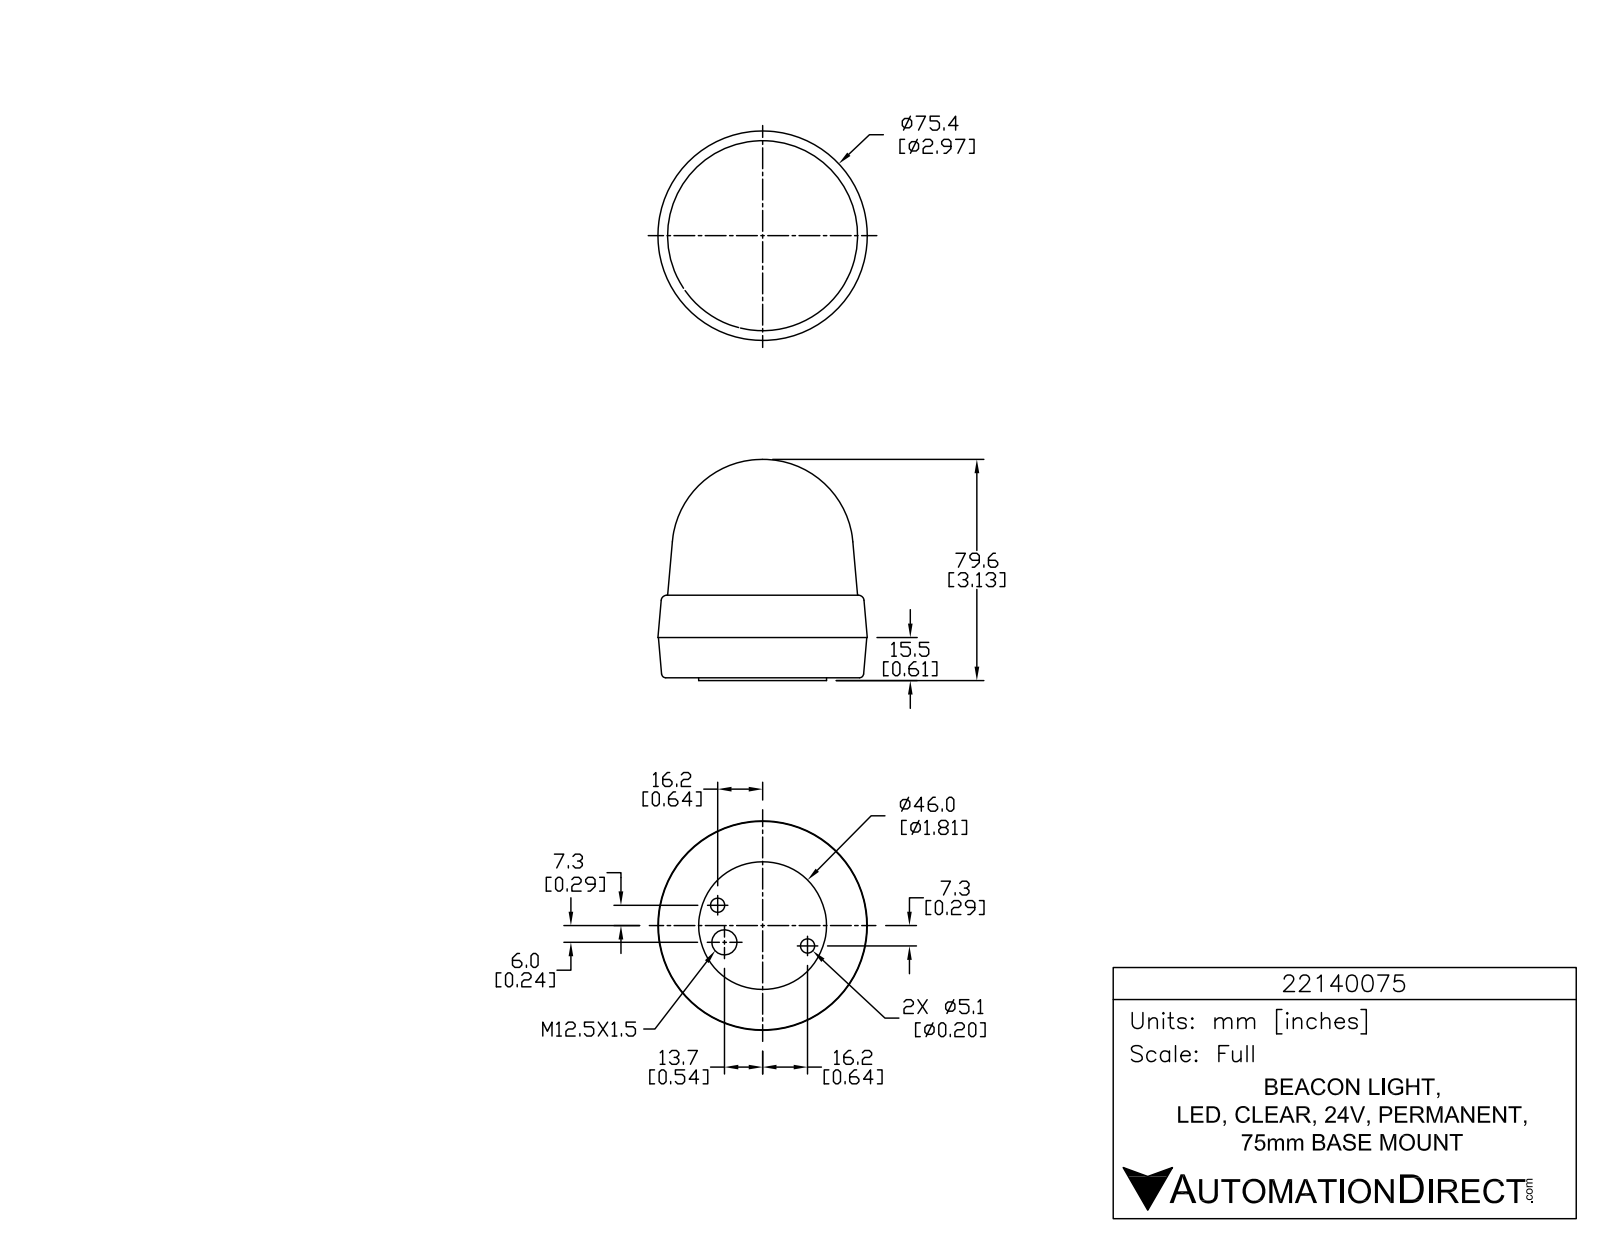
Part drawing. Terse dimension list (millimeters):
name: 22140075
written by: SolidWorks 2015 (AUTOMOTIVE_DESIGN)
unit: mm
bodies: 1 solid, 773 faces (526 planar, 163 cylindrical, 84 other)
size: 79.6 × 75.4 × 75.4
volume: 258 800 mm³; area: 21 740 mm²
holes: 3× ⌀1.5, 2× ⌀5.1, 1× ⌀9
bosses: 3× ⌀8.6, 3× ⌀2.1, 1× ⌀46
rounds: 9× R0.1, 6× R0.1, 6× R0.3, 6× R0.3, 6× R0.3, 6× R5, 3× R0.1, 3× R0.1
face distances: 1, 30.7, 29.7, 15.5, 14.5, 15.2, 39.8, 38.8, 24.3, 9.1
hole spacings: 13.6, 29.9, 35.5
